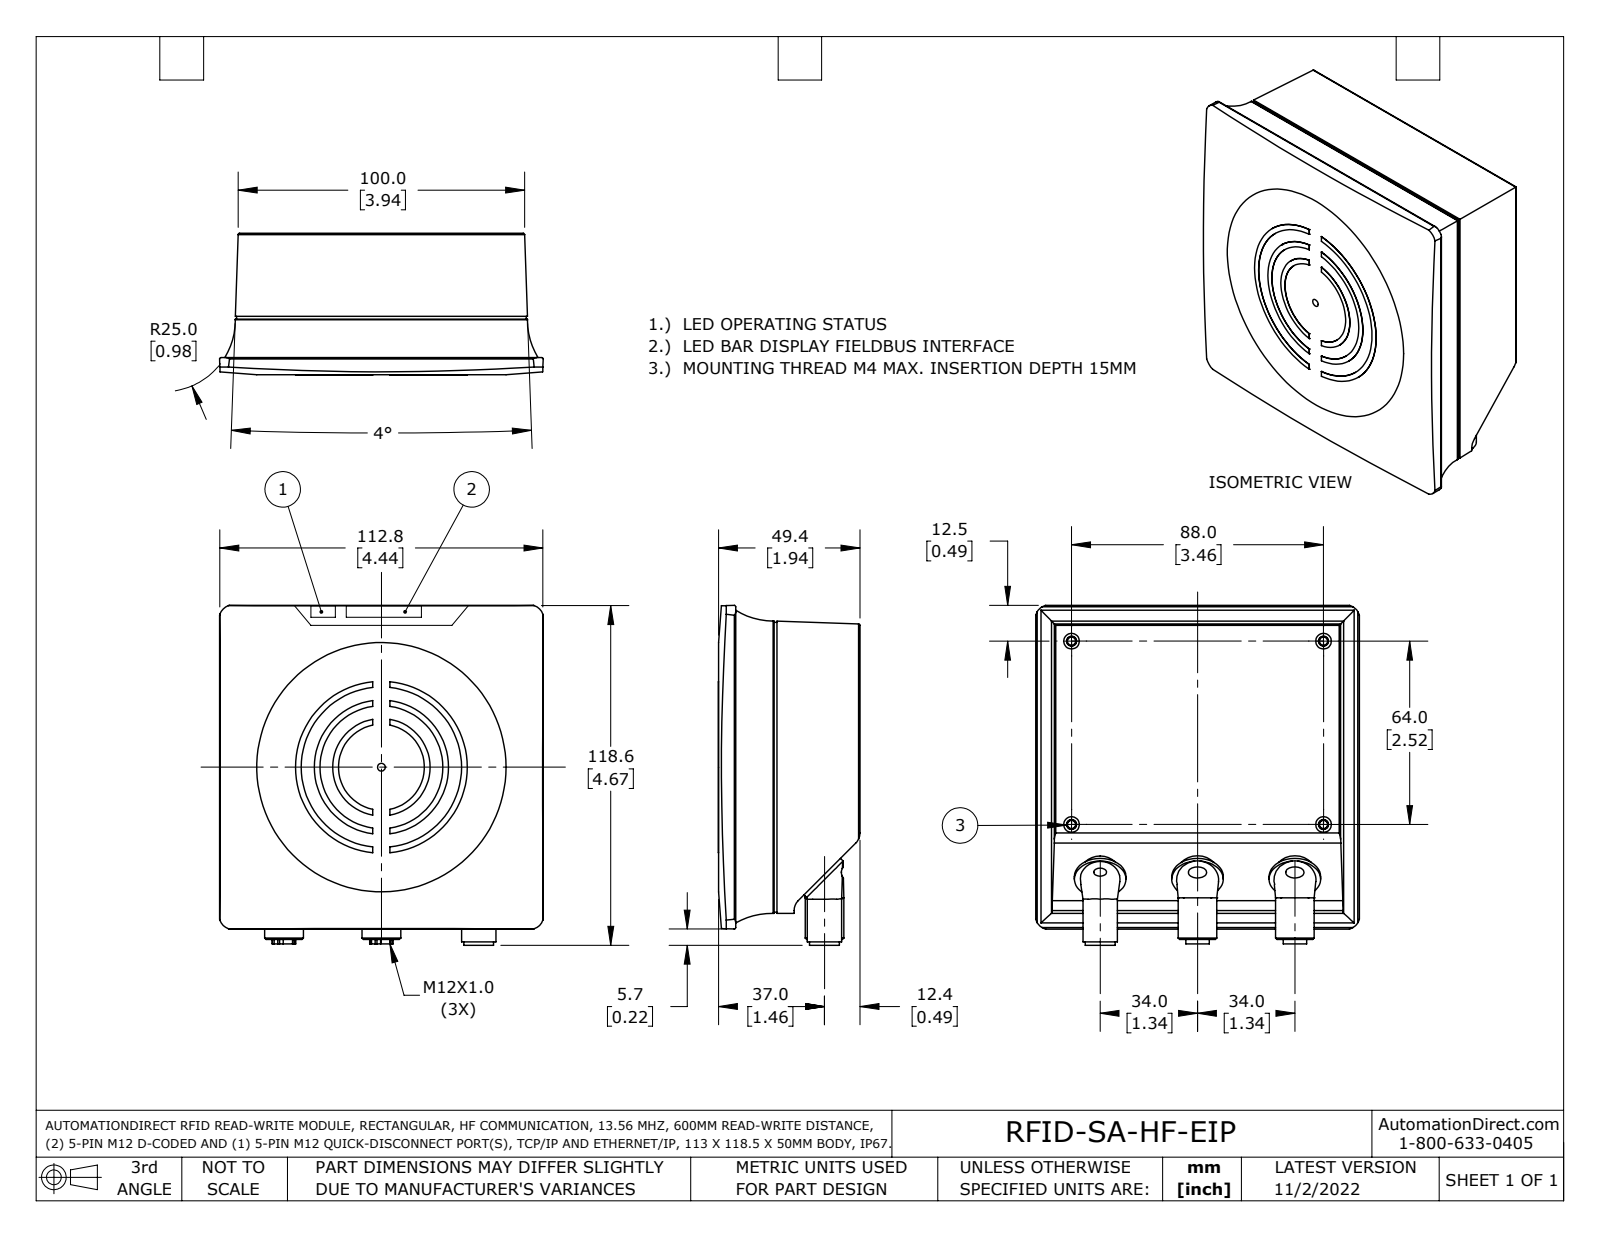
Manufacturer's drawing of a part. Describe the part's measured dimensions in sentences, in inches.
The part is named "RFID-SA-HF-EIP". Its 3-D file was written by "SolidWorks 2021 (AUTOMOTIVE_DESIGN)". It is 1 solid with 152 faces: 80 planar, 53 cylindrical and 19 other. Overall it measures 4.672 by 4.449 by 1.947 inches. Its volume is 30.39 cubic inches and its surface area 71.98 square inches. Round holes: 2 of diameter 0.398, 1 of diameter 0.327, 1 of diameter 1.181, 1 of diameter 1.689, 1 of diameter 2.205. Round bosses or shafts: 3 of diameter 0.709, 2 of diameter 0.531, 2 of diameter 0.323, 1 of diameter 2.362, 1 of diameter 1.846, 1 of diameter 1.339, 1 of diameter 0.472, 1 of diameter 0.409. Partial cylindrical surfaces (rounded edges, fillets, slot ends): 7 of radius 0.02, 4 of radius 0.012, 4 of radius 0.192, 4 of radius 0.984, 2 of radius 0.197, 1 of radius 0.022, 1 of radius 0.118. The main face-to-face distances are 1.945, 4.248, 1.947, 0.236, 1.709, 0.238, 4.249, 0.803, 3.984, 1.181. The hole center spacings are 1.339, 2.677.
